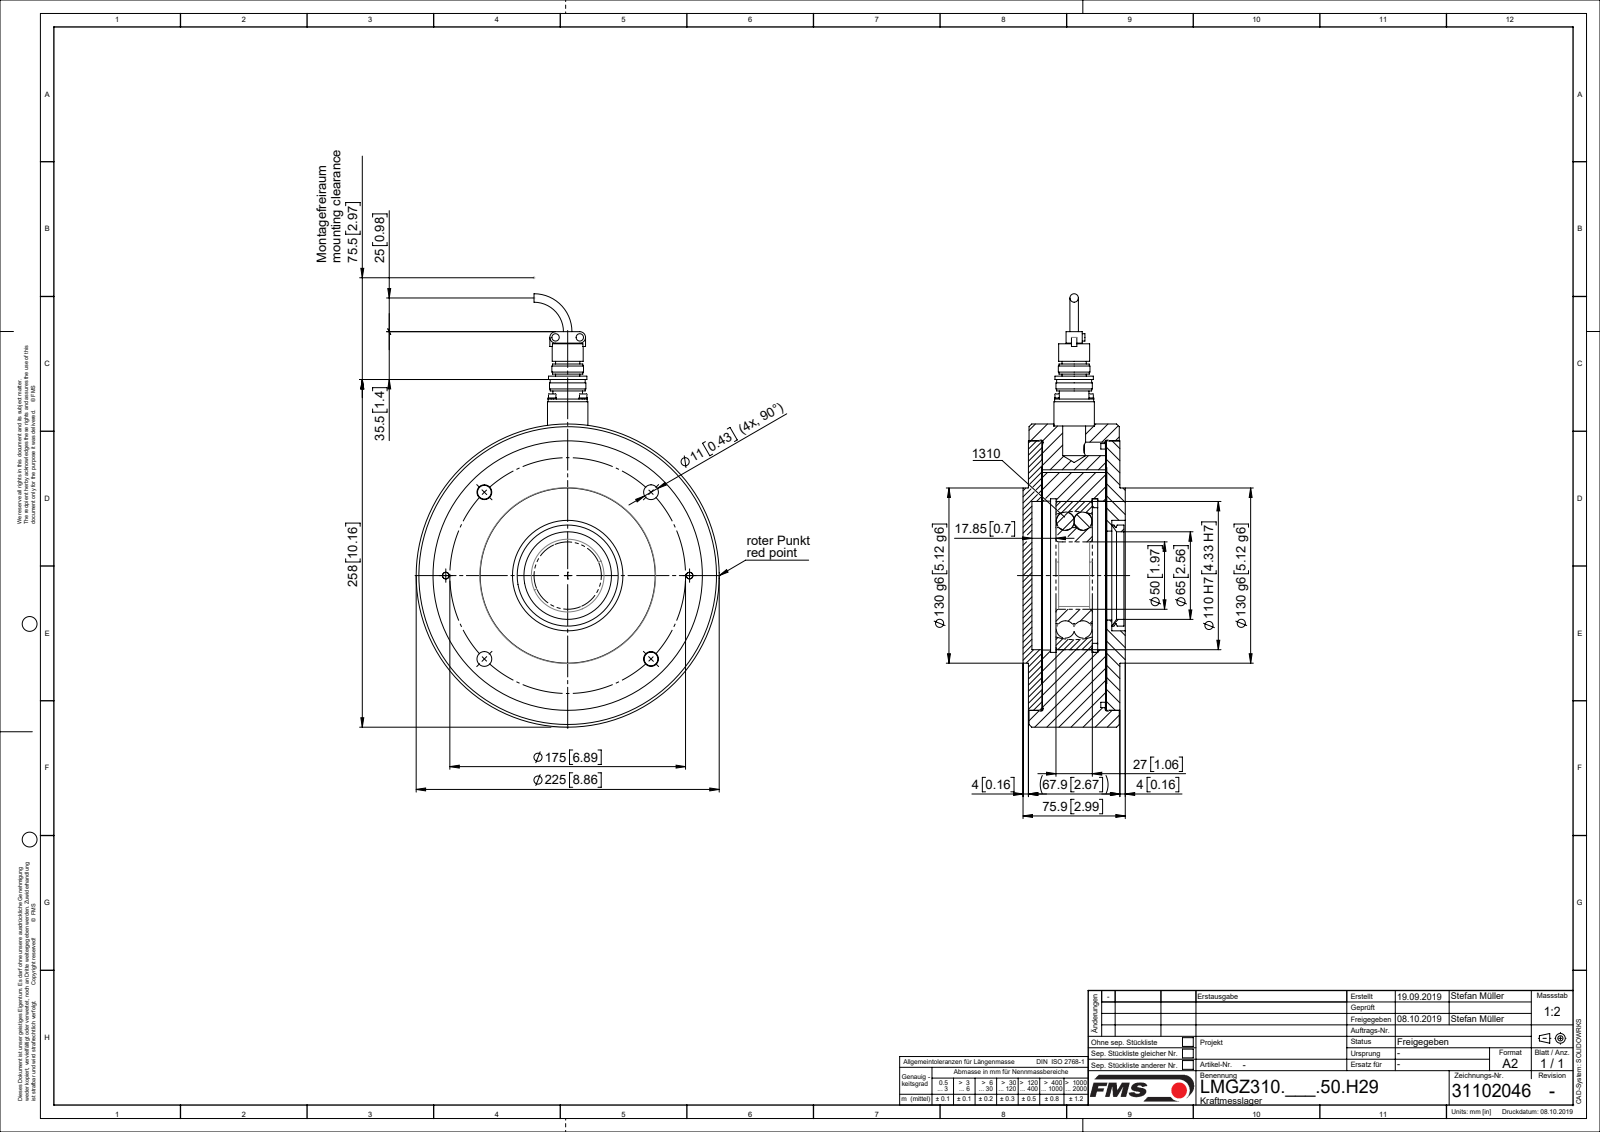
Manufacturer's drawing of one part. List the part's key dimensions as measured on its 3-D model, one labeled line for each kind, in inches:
Part name (STEP PRODUCT): L50007; L4765504; TEIL1; L49152 (+8 more)
STEP written by: Mechanical Desktop 2007 (CONFIG_CONTROL_DESIGN)
Units: inches
Bodies: 20 solids, 400 faces (112 planar, 232 cylindrical, 56 other)
Overall size (bounding box): 12.663 × 8.858 × 2.988
Volume: 146.8 in³ · Surface area: 606 in²
Round holes (diameter × count): ⌀0.433 ×6, ⌀0.102 ×4, ⌀0.126 ×4, ⌀0.134 ×4, ⌀0.354 ×4, ⌀0.197 ×2, ⌀0.26 ×2, ⌀0.906 ×1, ⌀1.969 ×1, ⌀2.52 ×1, ⌀2.598 ×1, ⌀3.228 ×1
Round bosses / shafts (diameter × count): ⌀0.217 ×6, ⌀0.244 ×4, ⌀0.118 ×4, ⌀0.098 ×4, ⌀0.394 ×2, ⌀0.236 ×2, ⌀8.858 ×1, ⌀7.835 ×1
Partial cylindrical surfaces — rounded edges, fillets, slot ends (radius × count): R0.167 ×2, R3.189 ×1, R3.386 ×1
Main face-to-face distances: 0.382, 1.86, 0.411, 0.423, 1.868, 0.402, 2.262, 2.272, 1.85, 0.394
Hole centre spacings: 0.64, 0.906, 2.684, 3.445, 4.872, 6.474, 1.281, 3.563
